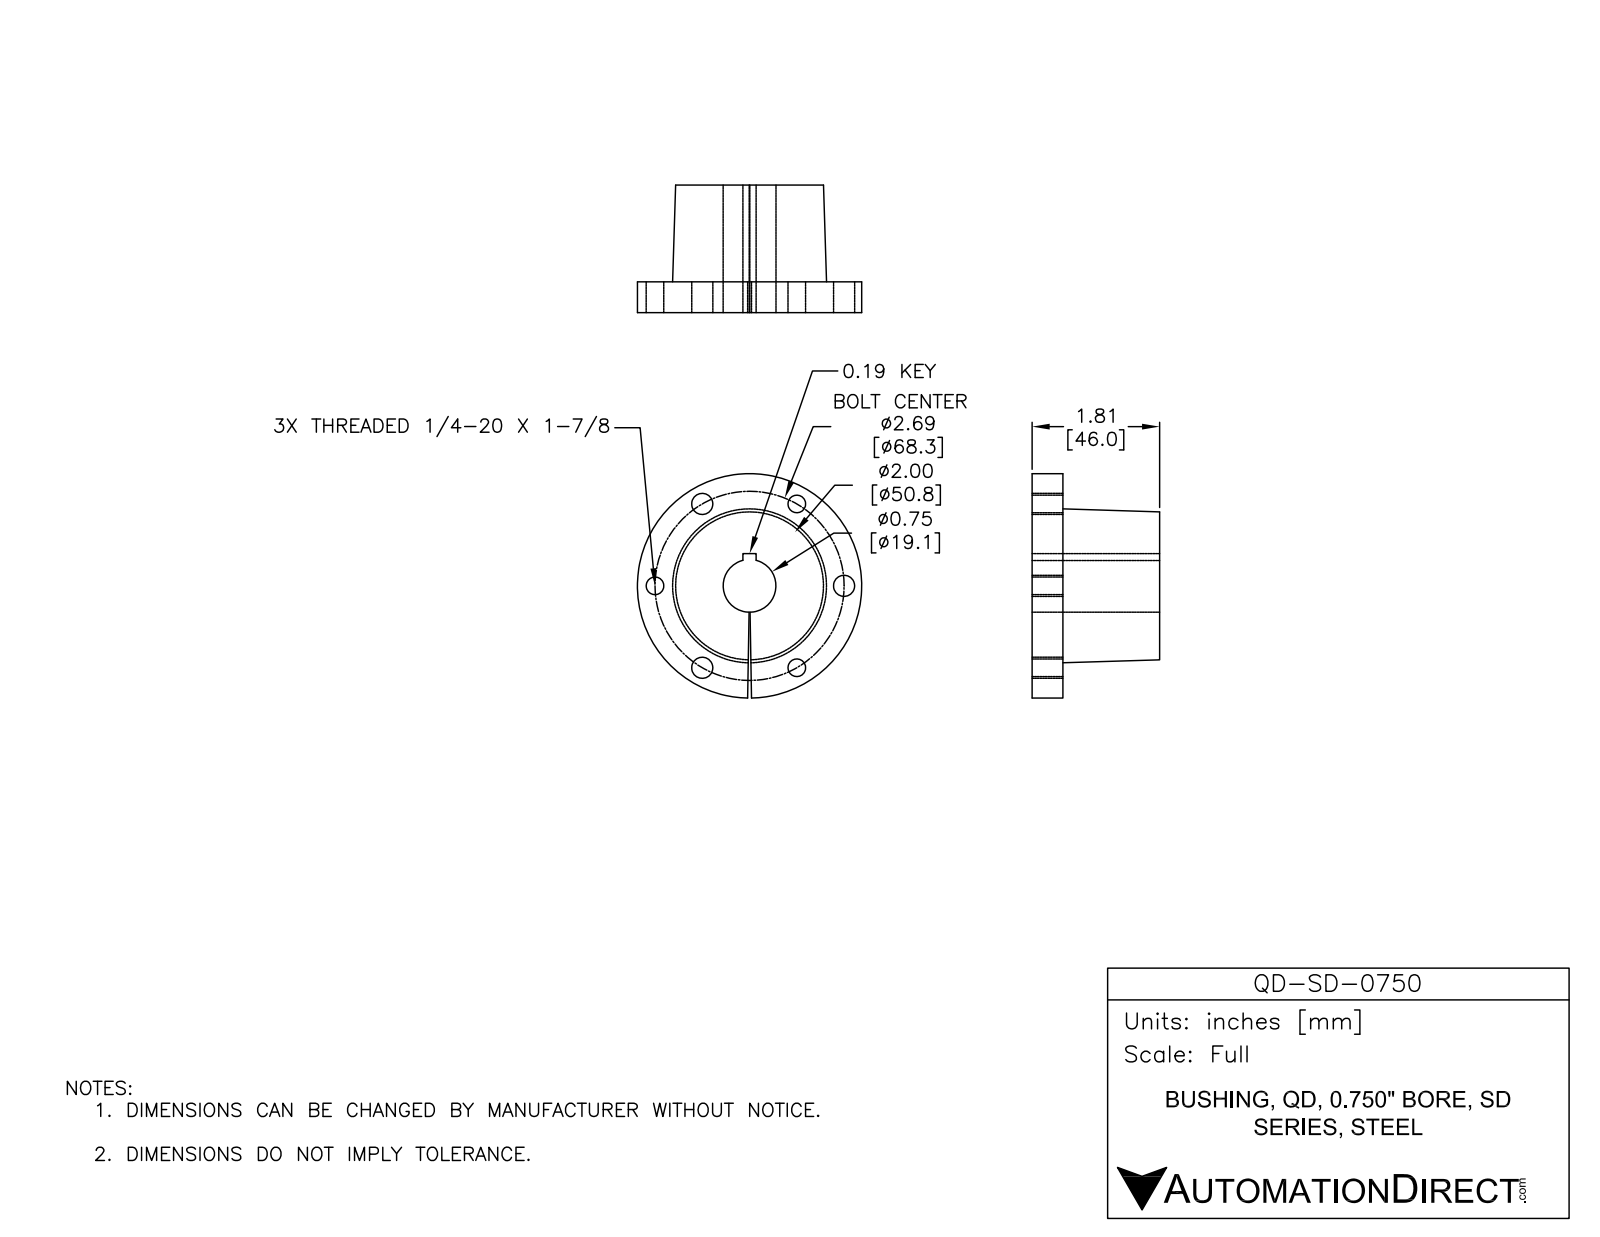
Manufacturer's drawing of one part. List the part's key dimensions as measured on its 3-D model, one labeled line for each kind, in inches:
Part name (STEP PRODUCT): QD-SD-0750
STEP written by: SolidWorks 2014 (AUTOMOTIVE_DESIGN)
Units: inches
Bodies: 1 solid, 29 faces (8 planar, 18 cylindrical, 3 other)
Overall size (bounding box): 3.188 × 3.187 × 1.813
Volume: 7.425 in³ · Surface area: 37.4 in²
Round holes (diameter × count): ⌀0.25 ×3, ⌀0.3 ×3, ⌀0.75 ×1
Round bosses / shafts (diameter × count): ⌀3.187 ×1
Main face-to-face distances: 0.437, 1.812, 1.375, 0.188
Hole centre spacings: 1.344, 2.328, 1.344, 2.688, 2.687
